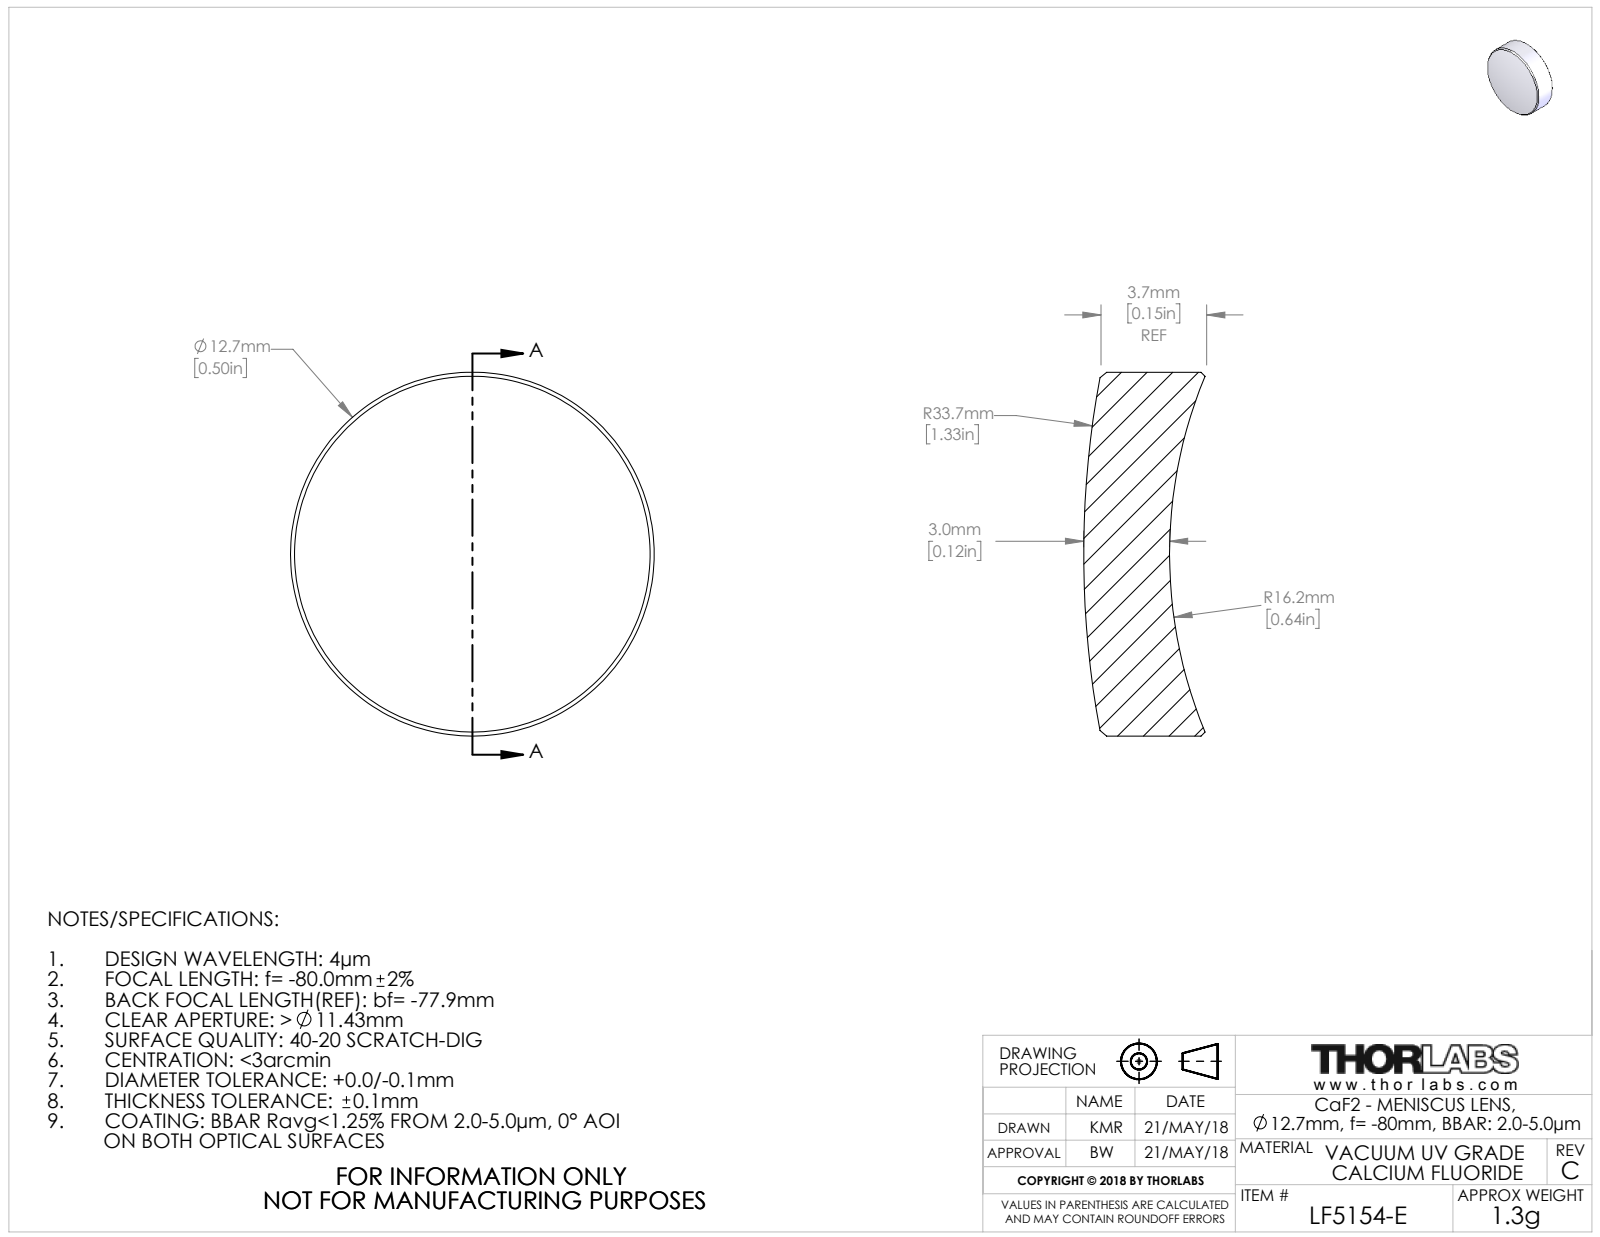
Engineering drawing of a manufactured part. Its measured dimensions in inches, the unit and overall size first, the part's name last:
Units: inches
Overall size (bounding box): 0.5 × 0.5 × 0.167
Round bosses / shafts (diameter × count): ⌀0.5 ×1
Volume: 0.026 in³ · Surface area: 0.616 in²
Bodies: 1 solid, 10 faces (0 planar, 2 cylindrical, 8 other)
Part name (STEP PRODUCT): 20183-E0W
STEP written by: SolidWorks 2016 (CONFIG_CONTROL_DESIGN)
